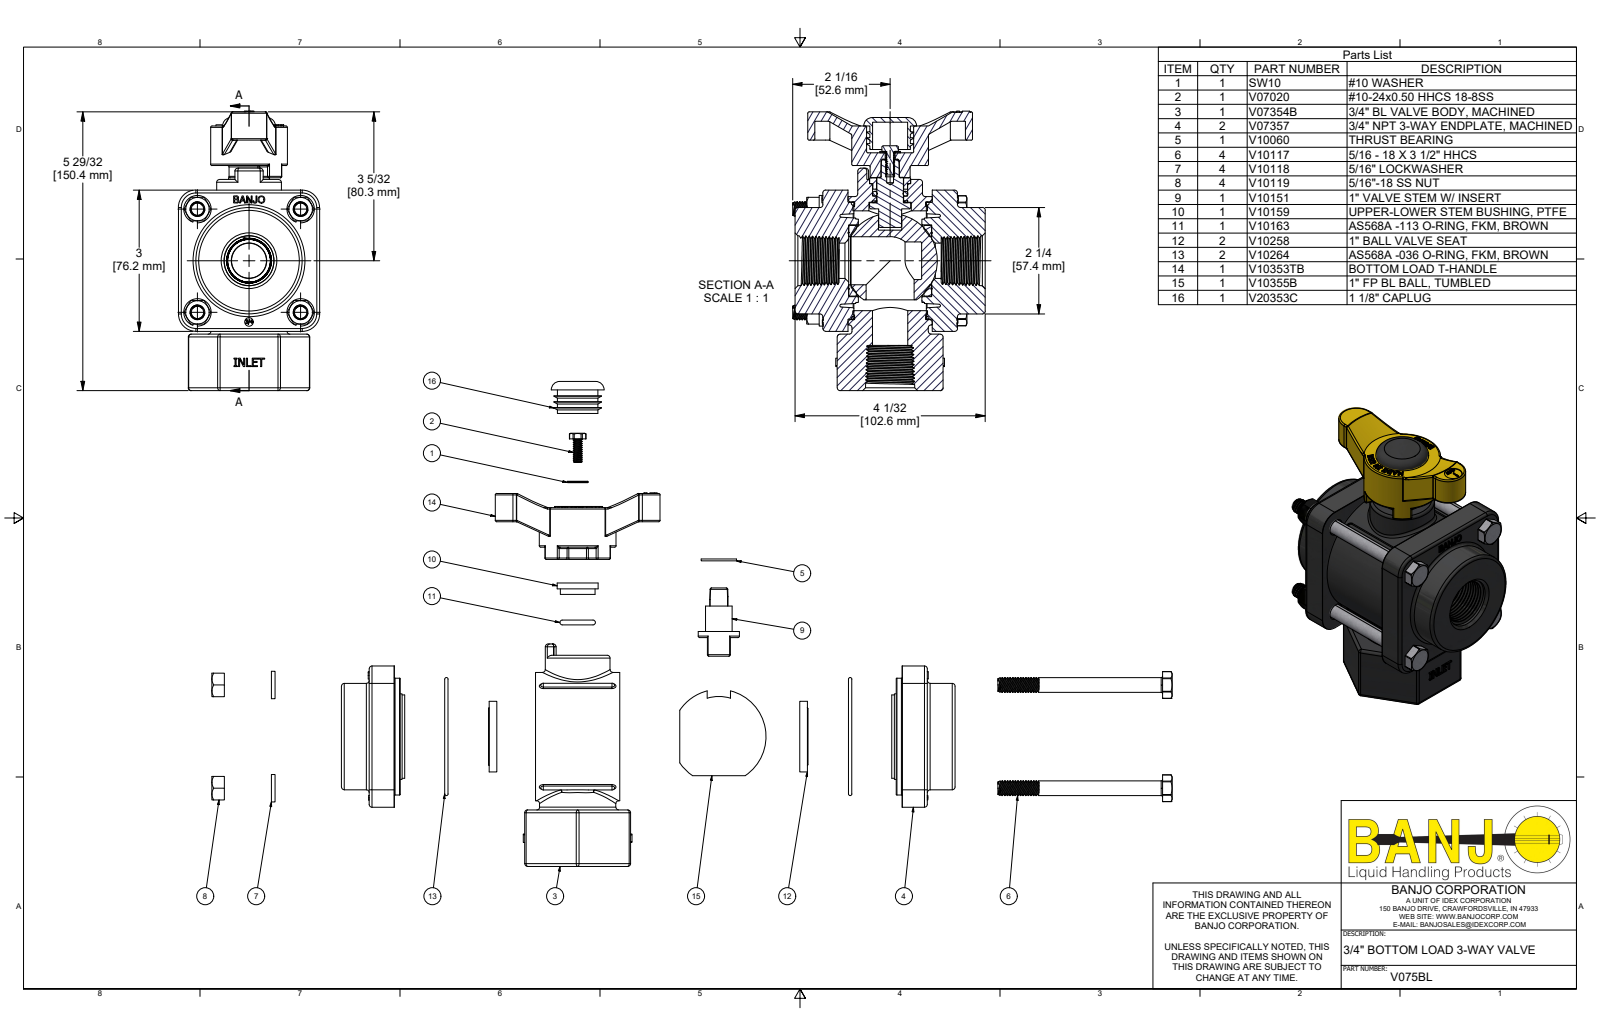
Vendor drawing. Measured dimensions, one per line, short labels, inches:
name: V075BL; V07354B; V07354BX; V07357 (+8 more)
written by: Autodesk Inventor 2022 (AUTOMOTIVE_DESIGN)
unit: in
bodies: 28 solids, 2520 faces (936 planar, 664 cylindrical, 920 other)
size: 5.935 × 4.09 × 3
volume: 28.58 in³; area: 219.6 in²
holes: 4× ⌀0.252, 4× ⌀0.322, 4× ⌀0.365, 2× ⌀0.75, 2× ⌀1.02, 1× ⌀0.091, 1× ⌀0.128, 1× ⌀0.145, 1× ⌀0.18, 1× ⌀0.203, 1× ⌀0.21, 1× ⌀0.375
bosses: 60× ⌀0.268, 4× ⌀0.583, 4× ⌀0.313, 1× ⌀2.725, 1× ⌀2.48, 1× ⌀2.302, 1× ⌀2.26, 1× ⌀1.77
rounds: 74× R0.03, 56× R0.06, 12× R0.031, 8× R0.134, 4× R0.096, 4× R0.284, 4× R0.37, 3× R0.016
face distances: 0.535, 2.325, 1.125, 0.59, 2.915, 3.45, 3, 1.79, 2.25, 2.86
hole spacings: 1.55, 2.192, 1.115, 2.635, 3.1, 0.663, 1.3, 1.533
